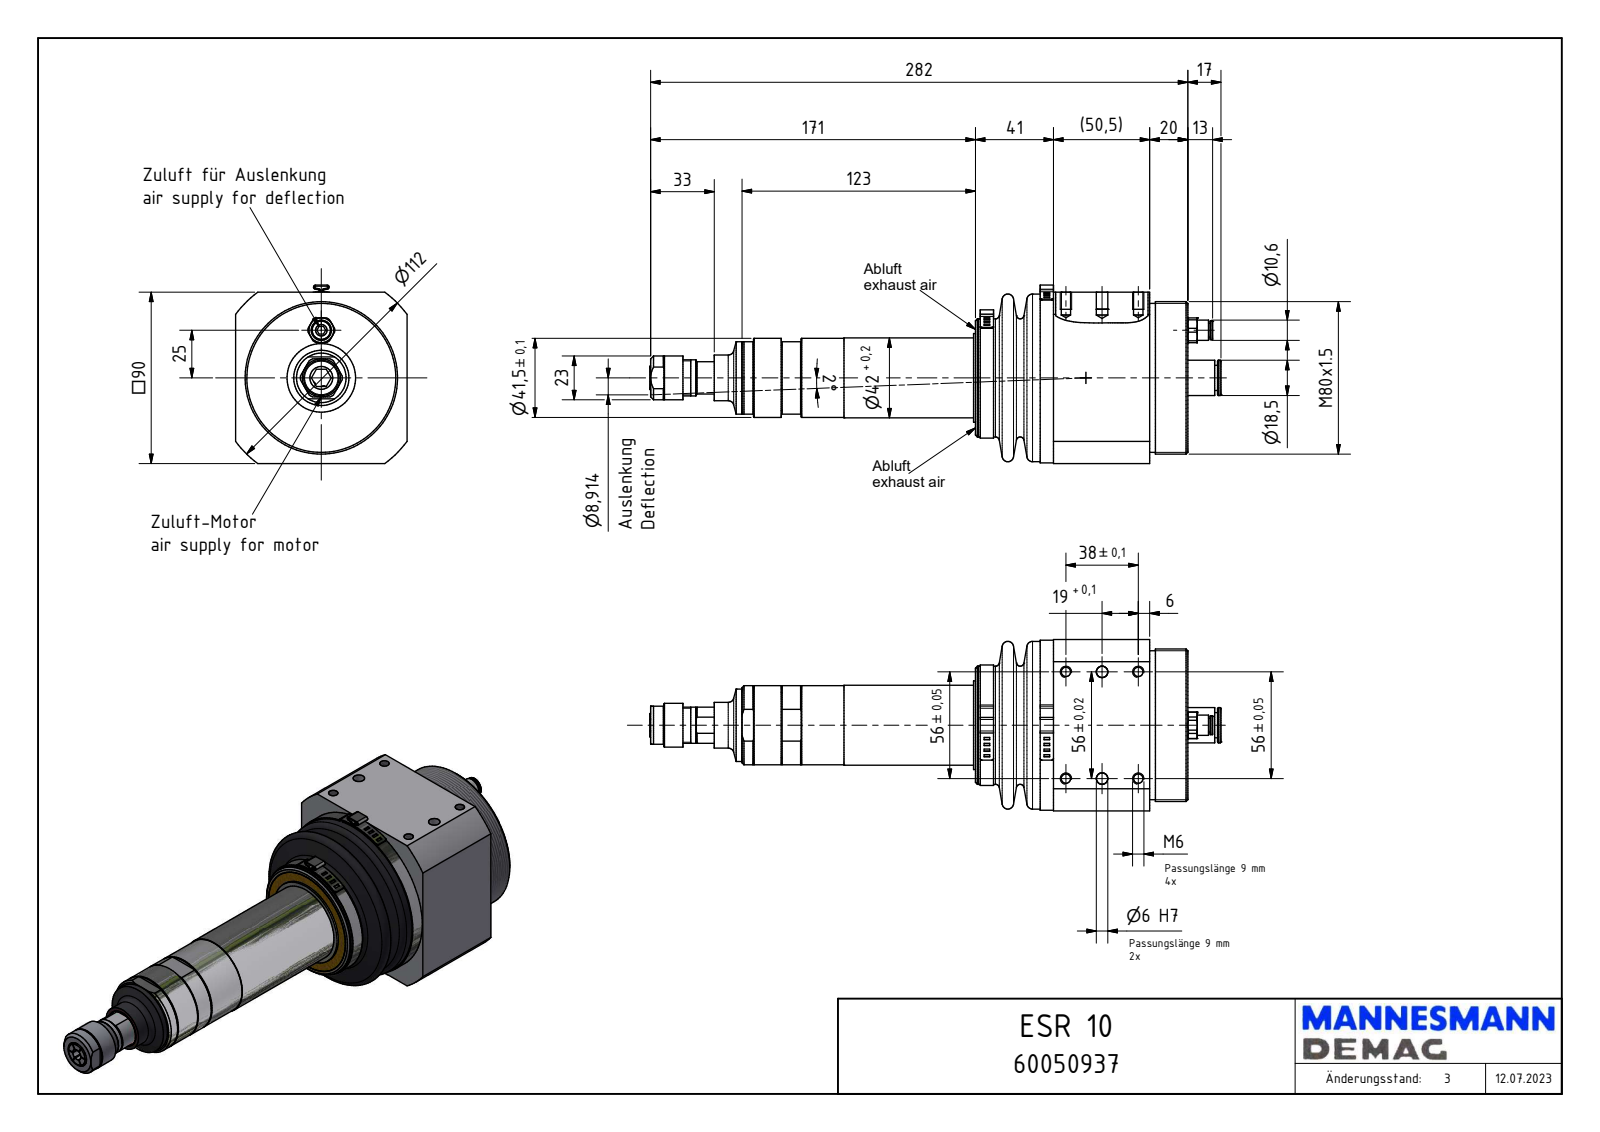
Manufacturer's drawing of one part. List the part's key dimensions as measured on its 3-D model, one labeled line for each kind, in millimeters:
Part name (STEP PRODUCT): ESR 10_60050937
STEP written by: Autodesk Inventor 2014 (CONFIG_CONTROL_DESIGN)
Units: millimetres
Bodies: 1 solid, 486 faces (223 planar, 148 cylindrical, 115 other)
Overall size (bounding box): 300.63 × 90 × 90
Volume: 810 418 mm³ · Surface area: 118 230 mm²
Round holes (diameter × count): ⌀4.92 ×4, ⌀6 ×4, ⌀1.6 ×1, ⌀2.5 ×1, ⌀8.57 ×1, ⌀10.5 ×1, ⌀12 ×1, ⌀17.92 ×1, ⌀19.5 ×1, ⌀36 ×1, ⌀65 ×1, ⌀70 ×1
Round bosses / shafts (diameter × count): ⌀89.2 ×1, ⌀88 ×1, ⌀78.16 ×1, ⌀63.2 ×1, ⌀62 ×1, ⌀60 ×1, ⌀59.5 ×1, ⌀46.5 ×1
Partial cylindrical surfaces — rounded edges, fillets, slot ends (radius × count): R0.5 ×8, R1 ×8, R1.1 ×8, R10 ×6, R18.09 ×6, R33.72 ×6, R1.4 ×4, R2 ×4
Main face-to-face distances: 90, 20, 50.5, 70.5, 3.5, 0.5, 37.5, 54, 74, 163.85
Hole centre spacings: 19, 59.14, 56, 28.04, 33.02, 34.7, 38, 67.68
